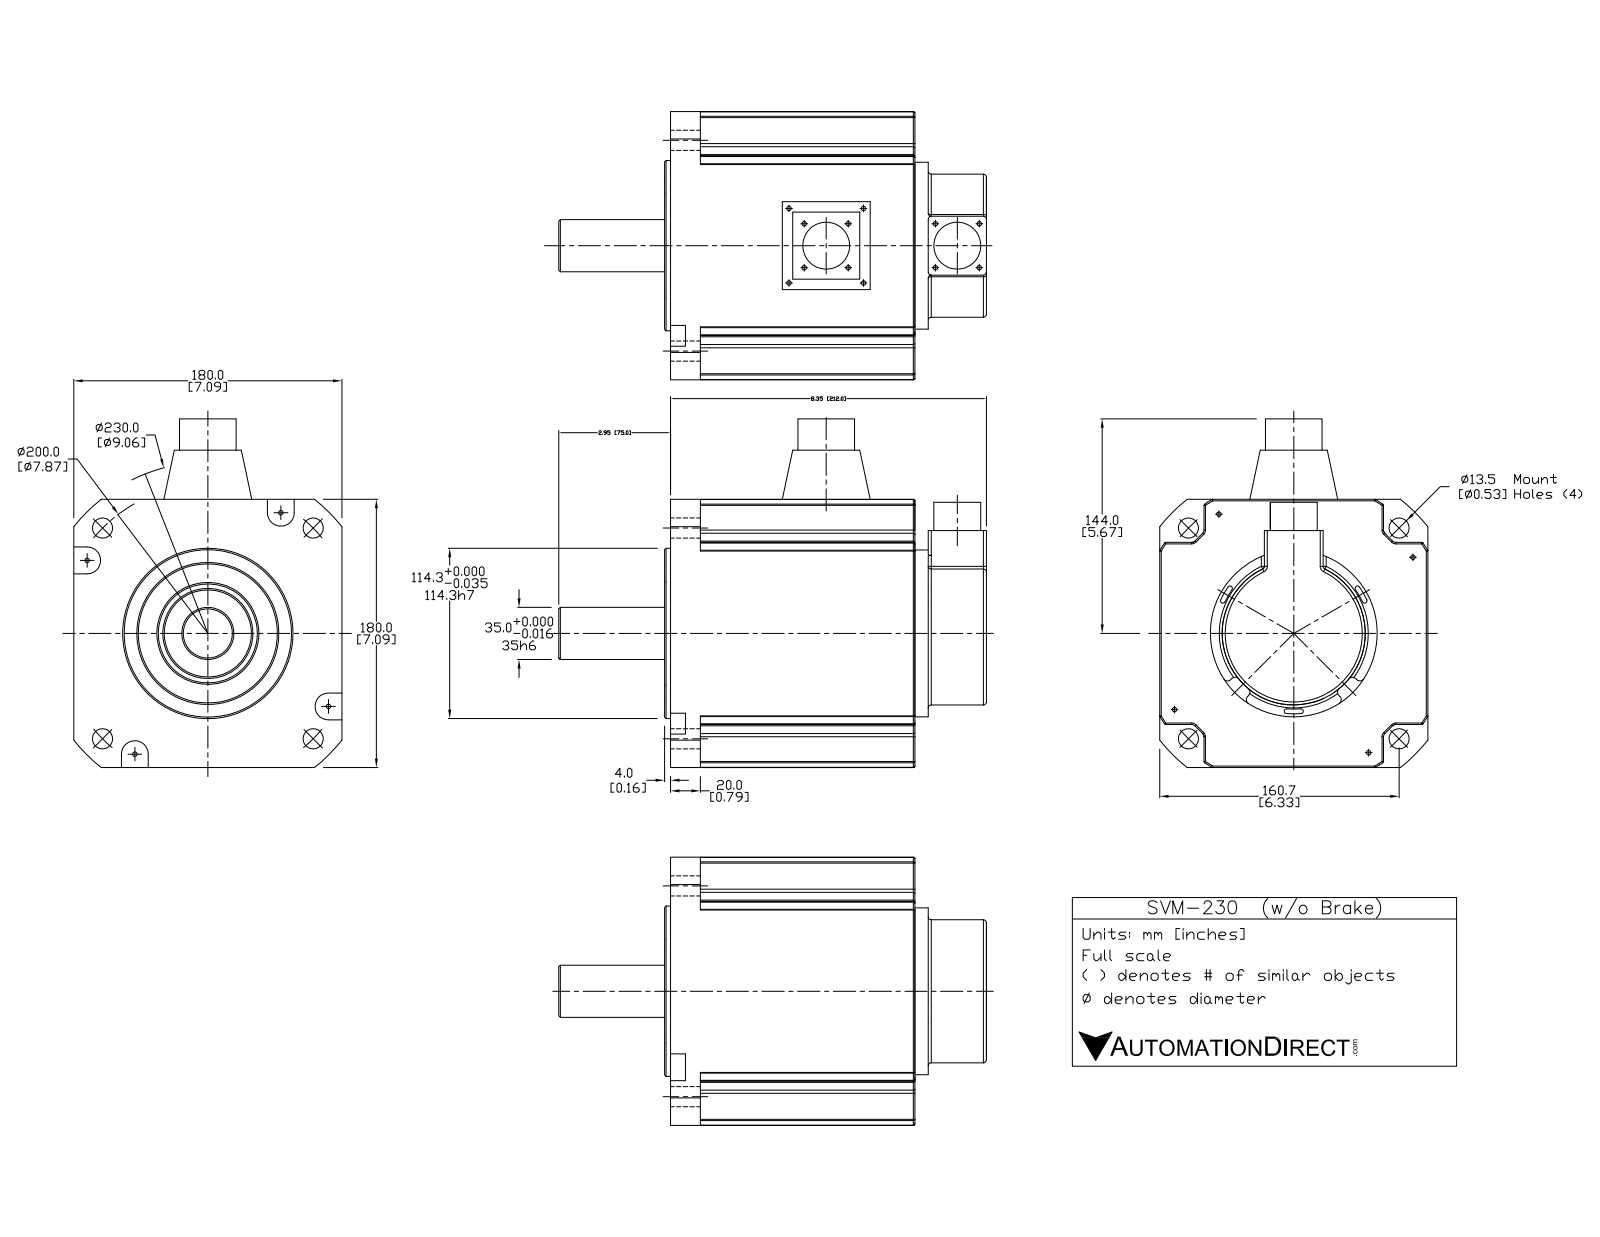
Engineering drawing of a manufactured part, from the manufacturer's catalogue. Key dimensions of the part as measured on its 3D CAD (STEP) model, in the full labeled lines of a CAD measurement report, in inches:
Part name (STEP PRODUCT): SVM-230
STEP written by: SolidWorks 2015 (AUTOMOTIVE_DESIGN)
Units: inches
Bodies: 32 solids, 460 faces (238 planar, 135 cylindrical, 87 other)
Overall size (bounding box): 11.299 × 9.213 × 7.087
Volume: 323.6 in³ · Surface area: 600.6 in²
Round holes (diameter × count): ⌀0.531 ×4, ⌀1.063 ×1, ⌀1.311 ×1, ⌀3.701 ×1
Round bosses / shafts (diameter × count): ⌀0.079 ×17, ⌀0.094 ×6, ⌀0.63 ×4, ⌀0.142 ×3, ⌀4.498 ×1, ⌀4.409 ×1, ⌀3.78 ×1, ⌀2.638 ×1
Partial cylindrical surfaces — rounded edges, fillets, slot ends (radius × count): R0.197 ×8, R0.039 ×4, R0.157 ×4, R0.236 ×4, R0.354 ×4, R2.559 ×1, R4.528 ×1
Main face-to-face distances: 4.685, 7.087, 0.609, 5.472, 0.787, 0.709, 1.219, 5.394, 6.181, 5.487
Hole centre spacings: 3.937, 5.568, 7.874, 3.48
